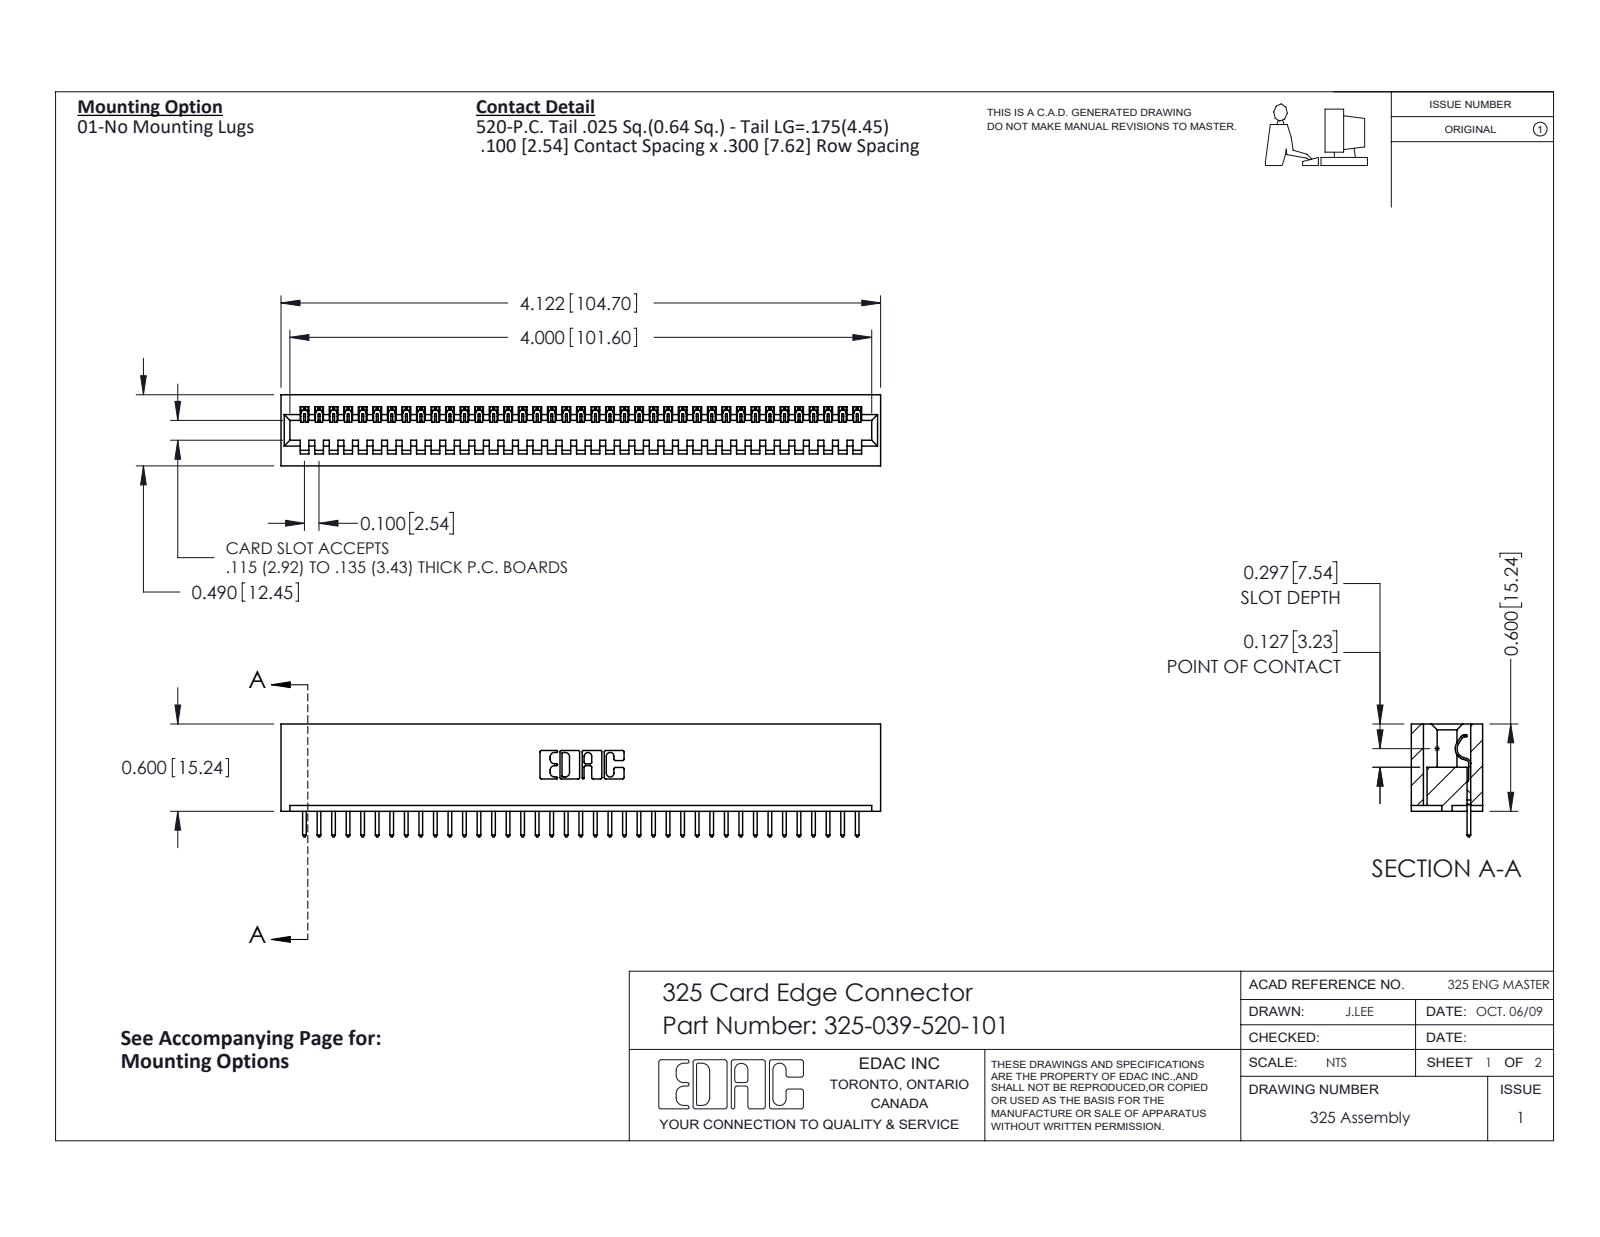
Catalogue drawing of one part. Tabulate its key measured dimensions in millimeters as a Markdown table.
| quantity | value |
| --- | --- |
| part name | 325 Part_Lugless; 325-039-520-101; 325-292-001_325-293-120 |
| STEP written by | SolidWorks 2016 (CONFIG_CONTROL_DESIGN) |
| units | millimeters |
| bodies | 40 solids, 2368 faces (1704 planar, 664 cylindrical, 0 other) |
| overall size | 104.7 × 19.7 × 12.4 |
| volume | 13 700 mm³ |
| surface area | 15 040 mm² |
| partial cylindrical surfaces (radius × count) | 0.2 × 78, 0.3 × 78, 0.3 × 22, 0.2 × 6, 0.8 × 6, 0.7 × 3, 0.4 × 1, 0.6 × 1 |
| main face-to-face distances | 2.1, 10.3, 12.4, 7.6, 2.7, 9.7, 0.6, 8.3, 14.2, 6.7 |
